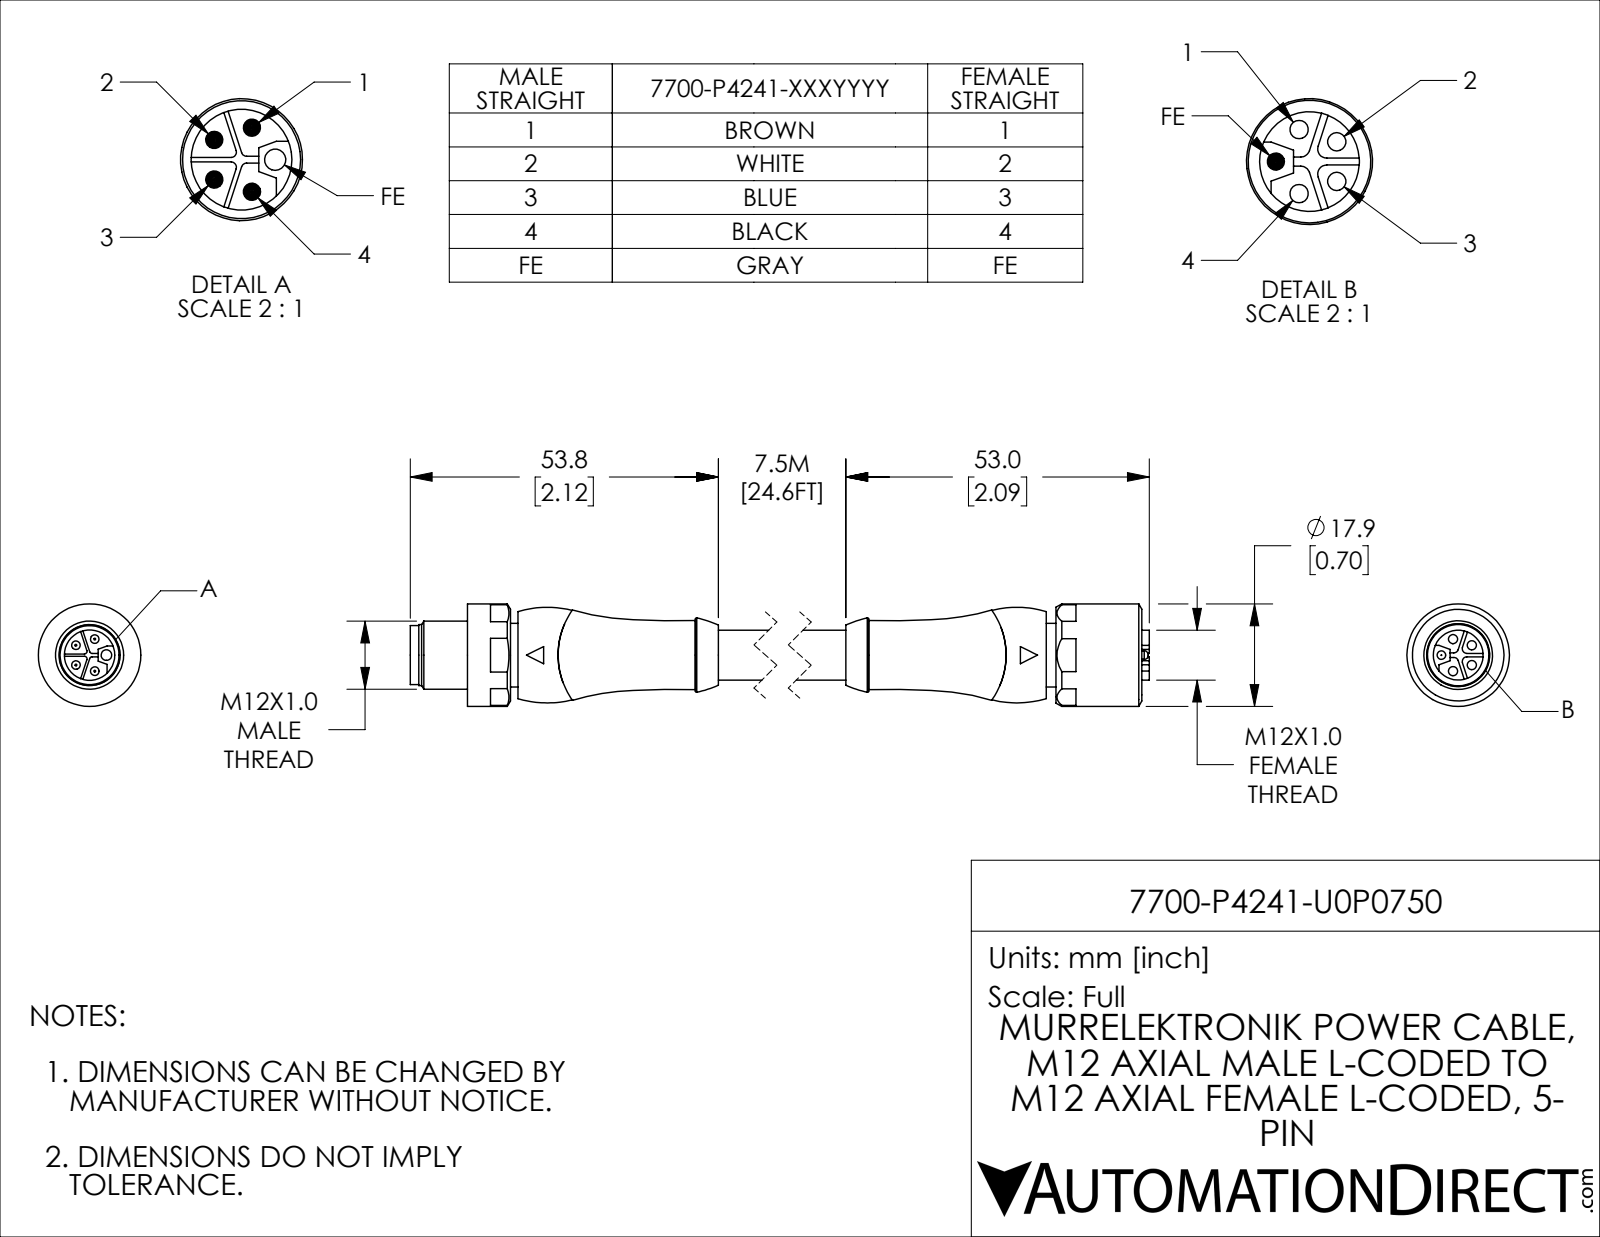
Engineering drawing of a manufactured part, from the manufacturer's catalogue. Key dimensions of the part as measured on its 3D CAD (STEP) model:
Part name (STEP PRODUCT): 7700-P4241-U0P0750_1; 7700-P4241-U0P0750; 7700-P4241-U0P0750_2
STEP written by: SolidWorks 2021 (CONFIG_CONTROL_DESIGN)
Units: inches
Bodies: 3 solids, 214 faces (98 planar, 62 cylindrical, 54 other)
Overall size (bounding box): 5.386 × 0.705 × 0.705
Volume: 1.09 in³ · Surface area: 14.44 in²
Round holes (diameter × count): ⌀0.063 ×4, ⌀0.073 ×1, ⌀0.346 ×1, ⌀0.433 ×1, ⌀0.512 ×1
Round bosses / shafts (diameter × count): ⌀0.059 ×5, ⌀0.705 ×1, ⌀0.51 ×1, ⌀0.469 ×1, ⌀0.437 ×1, ⌀0.419 ×1, ⌀0.406 ×1, ⌀0.343 ×1
Partial cylindrical surfaces — rounded edges, fillets, slot ends (radius × count): R0.018 ×4, R0.031 ×4
Main face-to-face distances: 4.283, 0.067, 0.346, 0.666, 0.051, 0.295, 0.228, 4.941, 0.657, 4.35
Hole centre spacings: 0.116, 0.136, 0.22, 0.22
